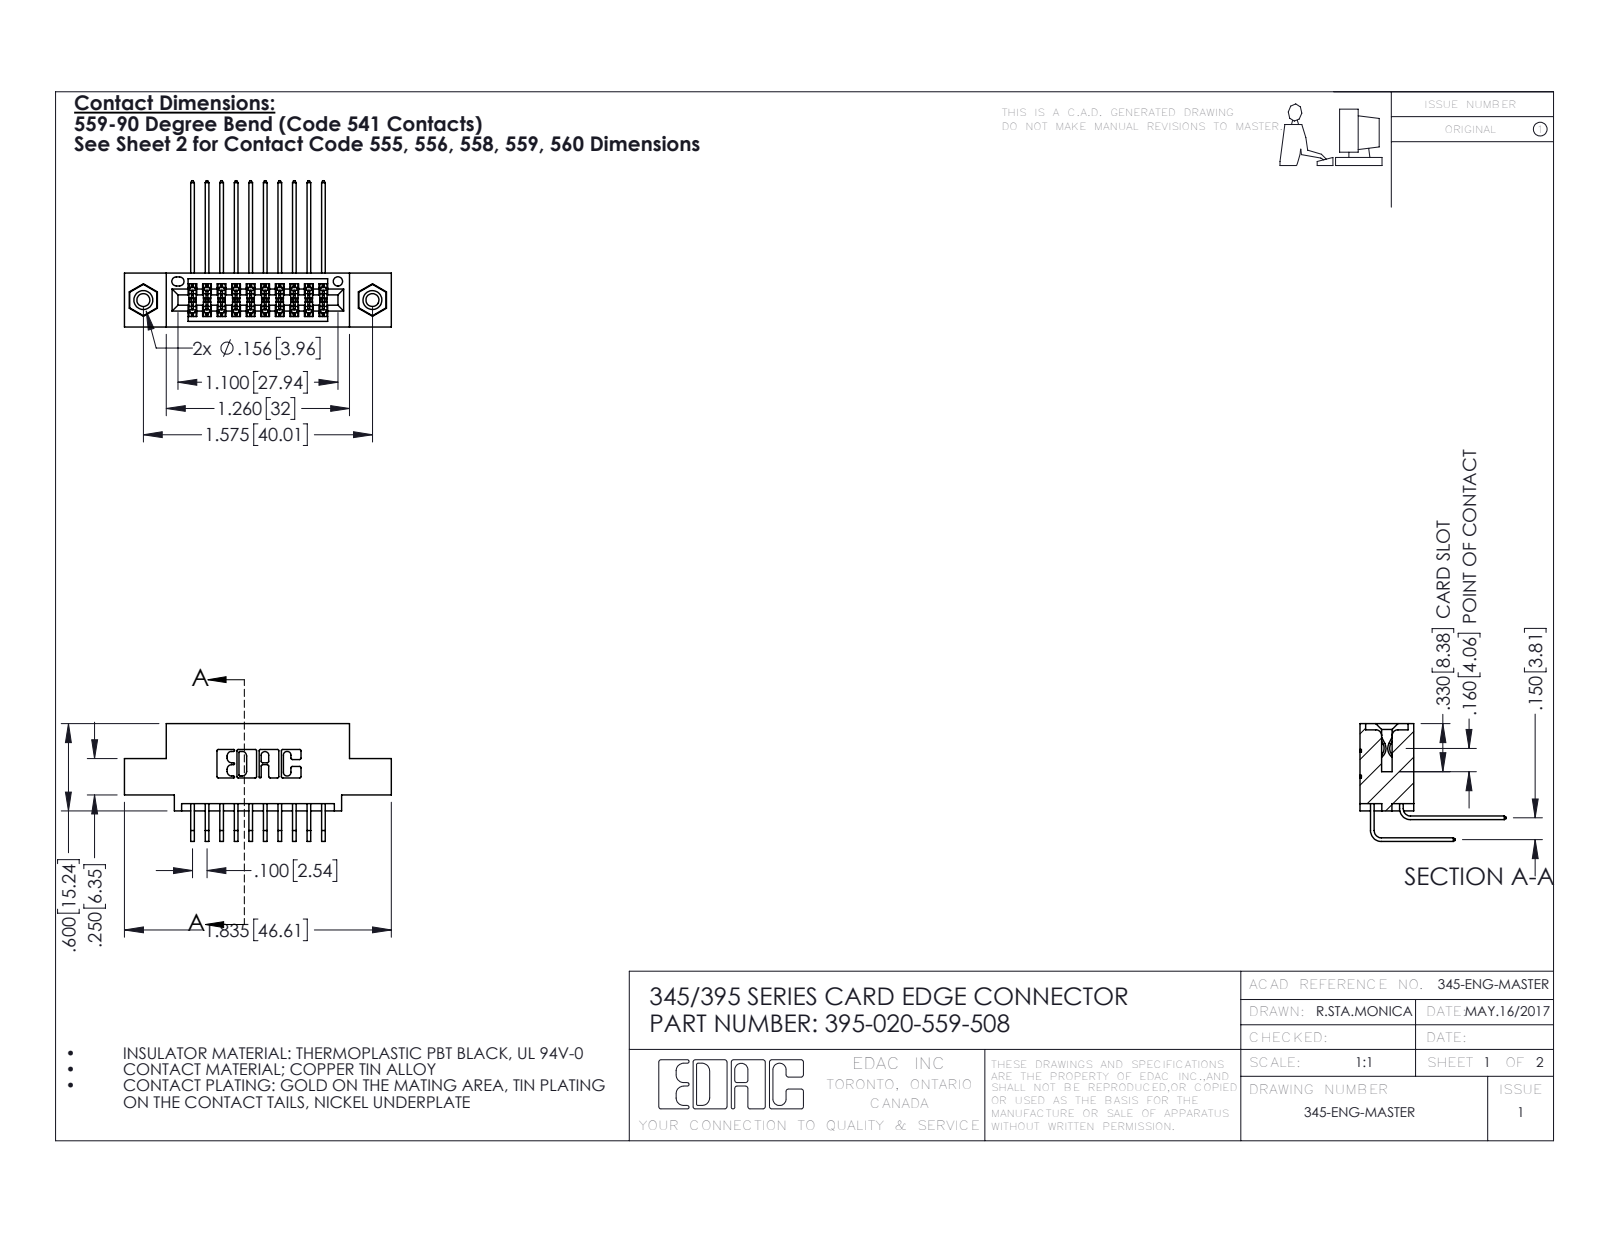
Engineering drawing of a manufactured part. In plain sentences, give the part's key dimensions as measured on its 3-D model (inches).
The part is named "395-020-559-508; 345 Part_0.110 Offset - 0.156 Dia-TI; 345-292-001_558 559 Tail - 1; 345-292-001_559 Tail - 2 (+1 more)". Its 3-D file was written by "SolidWorks 2016 (CONFIG_CONTROL_DESIGN)". It is 23 solids with 1230 faces: 816 planar, 398 cylindrical and 16 other. Overall it measures 1.835 by 1.005 by 0.809 inches. Its volume is 0.26 cubic inches and its surface area 9.819 square inches. Round holes: 2 of diameter 0.089, 2 of diameter 0.125, 2 of diameter 0.156, 1 of diameter 0.064. Round bosses or shafts: 2 of diameter 0.155. Partial cylindrical surfaces (rounded edges, fillets, slot ends): 31 of radius 0.006, 22 of radius 0.01, 6 of radius 0.007, 6 of radius 0.031, 3 of radius 0.026, 2 of radius 0.014, 2 of radius 0.019, 2 of radius 0.022. The main face-to-face distances are 0.2, 0.072, 0.298, 0.37, 0.1, 0.098, 0.272, 0.025, 0.6, 0.15. The hole center spacings are 0.27, 1.344, 1.575.
